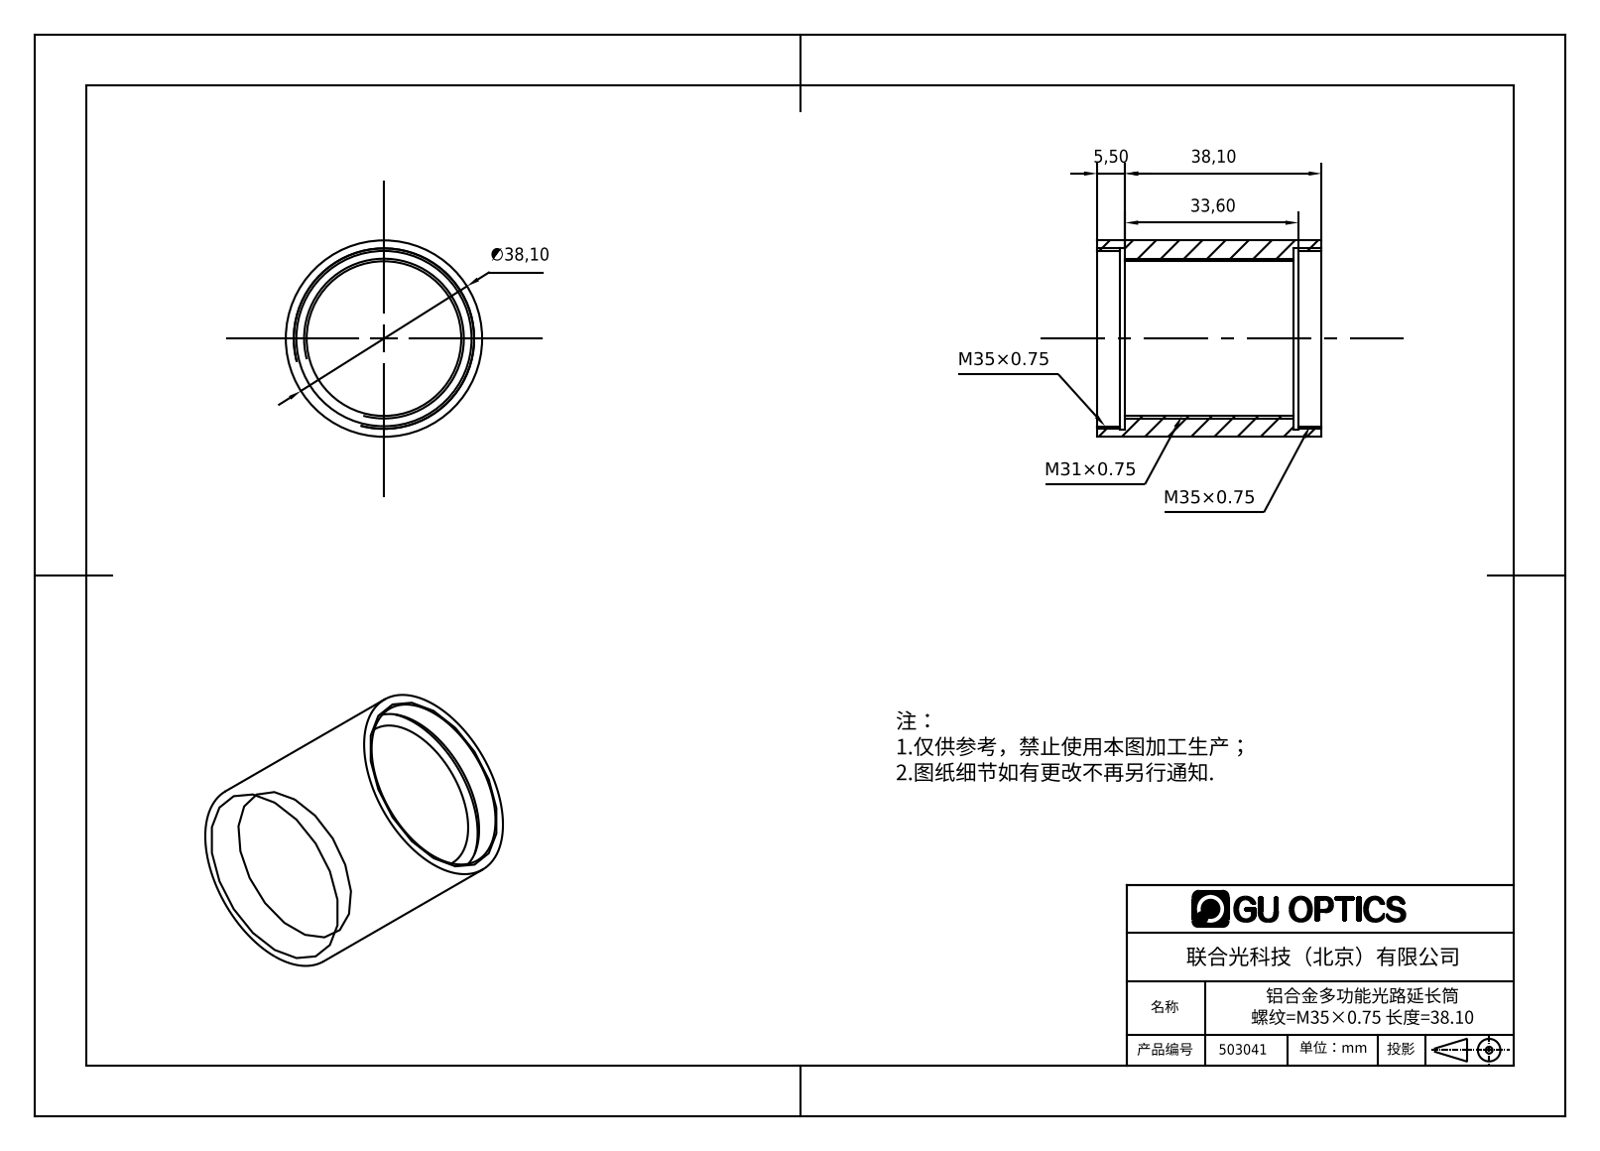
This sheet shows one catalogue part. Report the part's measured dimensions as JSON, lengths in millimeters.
{"part_name": "503041", "step_written_by": "SolidWorks 2016 (AUTOMOTIVE_DESIGN)", "units": "millimeters", "bodies": {"solids": 1, "faces": 18, "planar": 6, "cylindrical": 12, "other": 0}, "overall_size": [43.6, 38.1, 38.1], "volume_mm3": 16547, "surface_area_mm2": 10601, "round_holes": [[30, 1], [34, 1], [35.2, 1]], "round_bosses_or_shafts": [[38.1, 1]], "face_to_face_distances": [5.5, 38.1, 32.6, 43.6, 4.5, 39.1, 1, 33.6, 34.6]}
